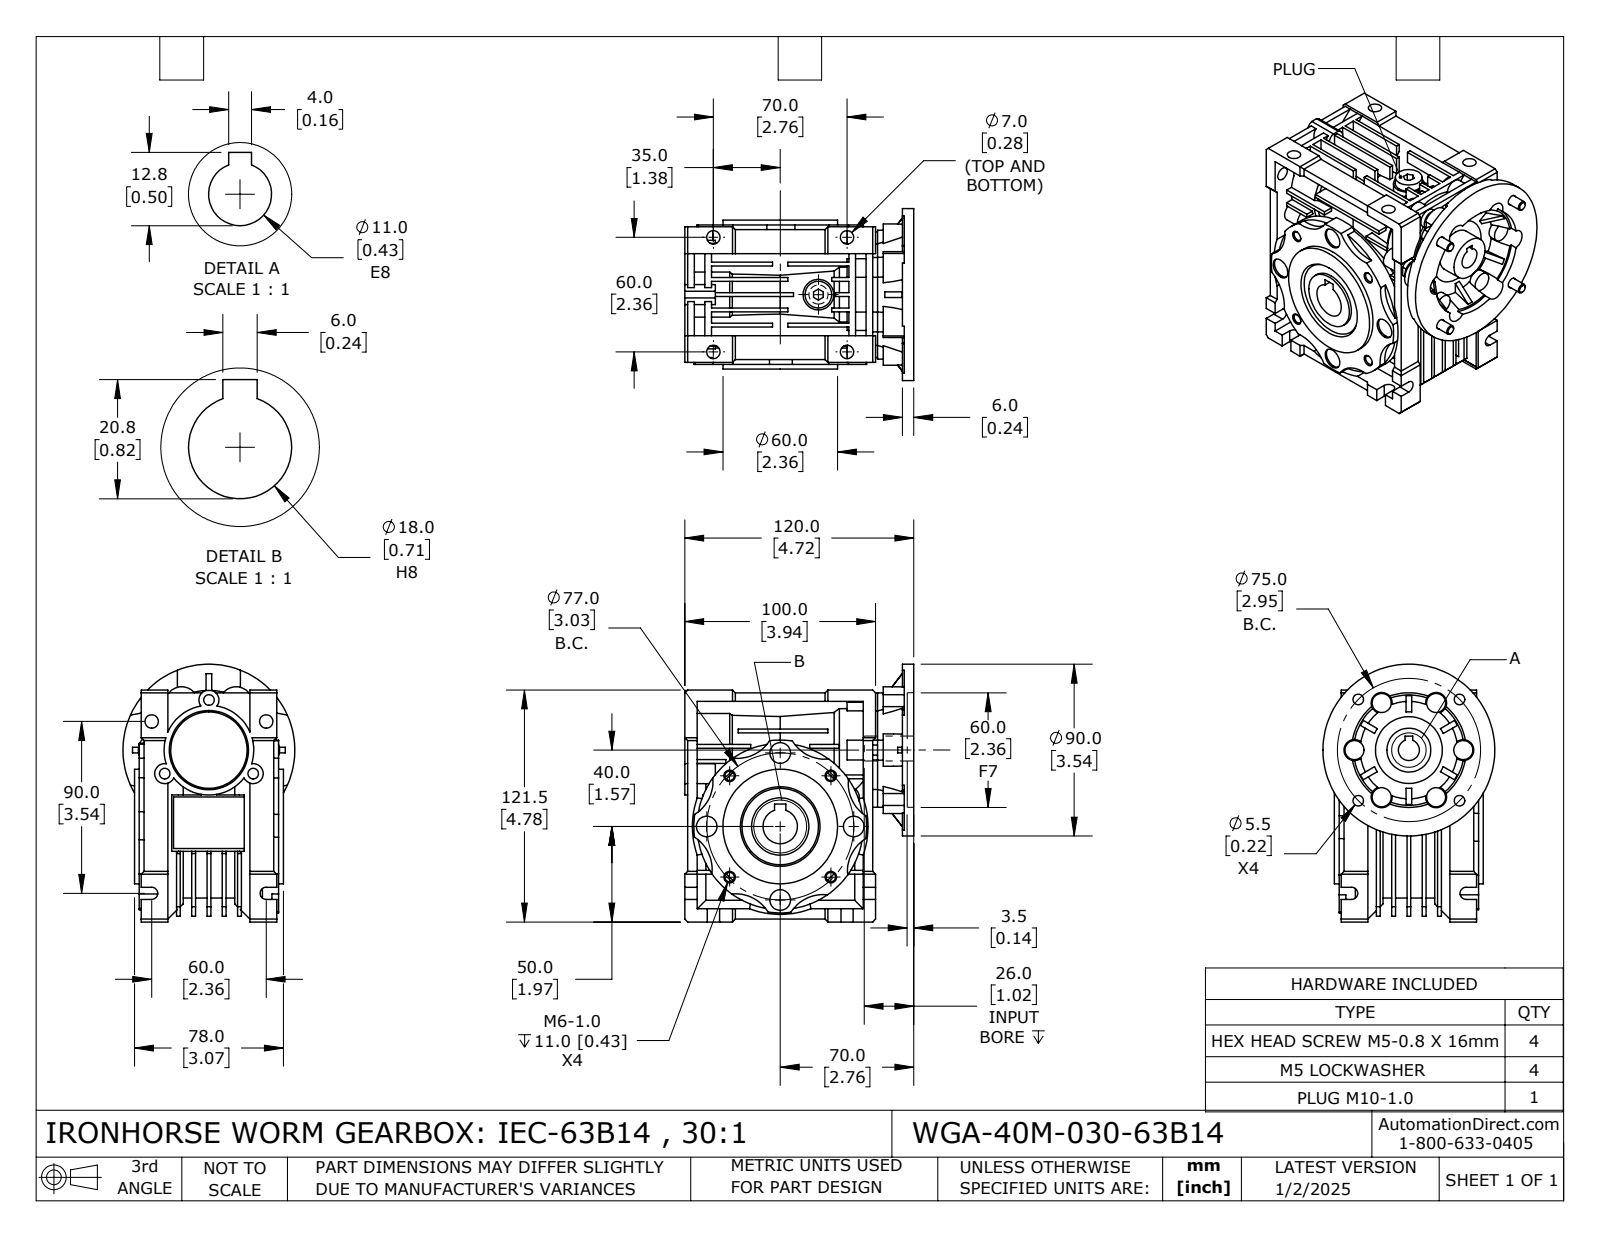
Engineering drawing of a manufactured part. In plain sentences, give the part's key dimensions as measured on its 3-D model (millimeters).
The part is named "WGA-40M-030-63B14". Its 3-D file was written by "SolidWorks 2024 (CONFIG_CONTROL_DESIGN)". It is 14 solids with 1003 faces: 564 planar, 307 cylindrical and 132 other. Overall it measures 135 by 127.7 by 90 millimeters. Its volume is 667 307 cubic millimeters and its surface area 163 100 square millimeters. Round holes: 6 of diameter 7, 4 of diameter 4.92, 4 of diameter 5.1, 4 of diameter 5.5, 4 of diameter 10.8, 3 of diameter 5.55, 1 of diameter 9, 1 of diameter 11, 1 of diameter 11.5, 1 of diameter 18, 1 of diameter 23, 1 of diameter 28. Round bosses or shafts: 6 of diameter 10, 4 of diameter 9.2, 4 of diameter 5, 1 of diameter 90, 1 of diameter 75, 1 of diameter 60, 1 of diameter 54, 1 of diameter 47. Partial cylindrical surfaces (rounded edges, fillets, slot ends): 9 of radius 5.25, 8 of radius 20, 6 of radius 3.2, 6 of radius 5.22, 6 of radius 5.5, 6 of radius 8.5, 4 of radius 5.51, 1 of radius 30. The main face-to-face distances are 8, 6, 2, 1.5, 16, 10, 5, 14, 2.5, 19. The hole center spacings are 29.1, 37.5, 53.04, 70.22, 33.54, 38.5, 54.45, 75.01.
